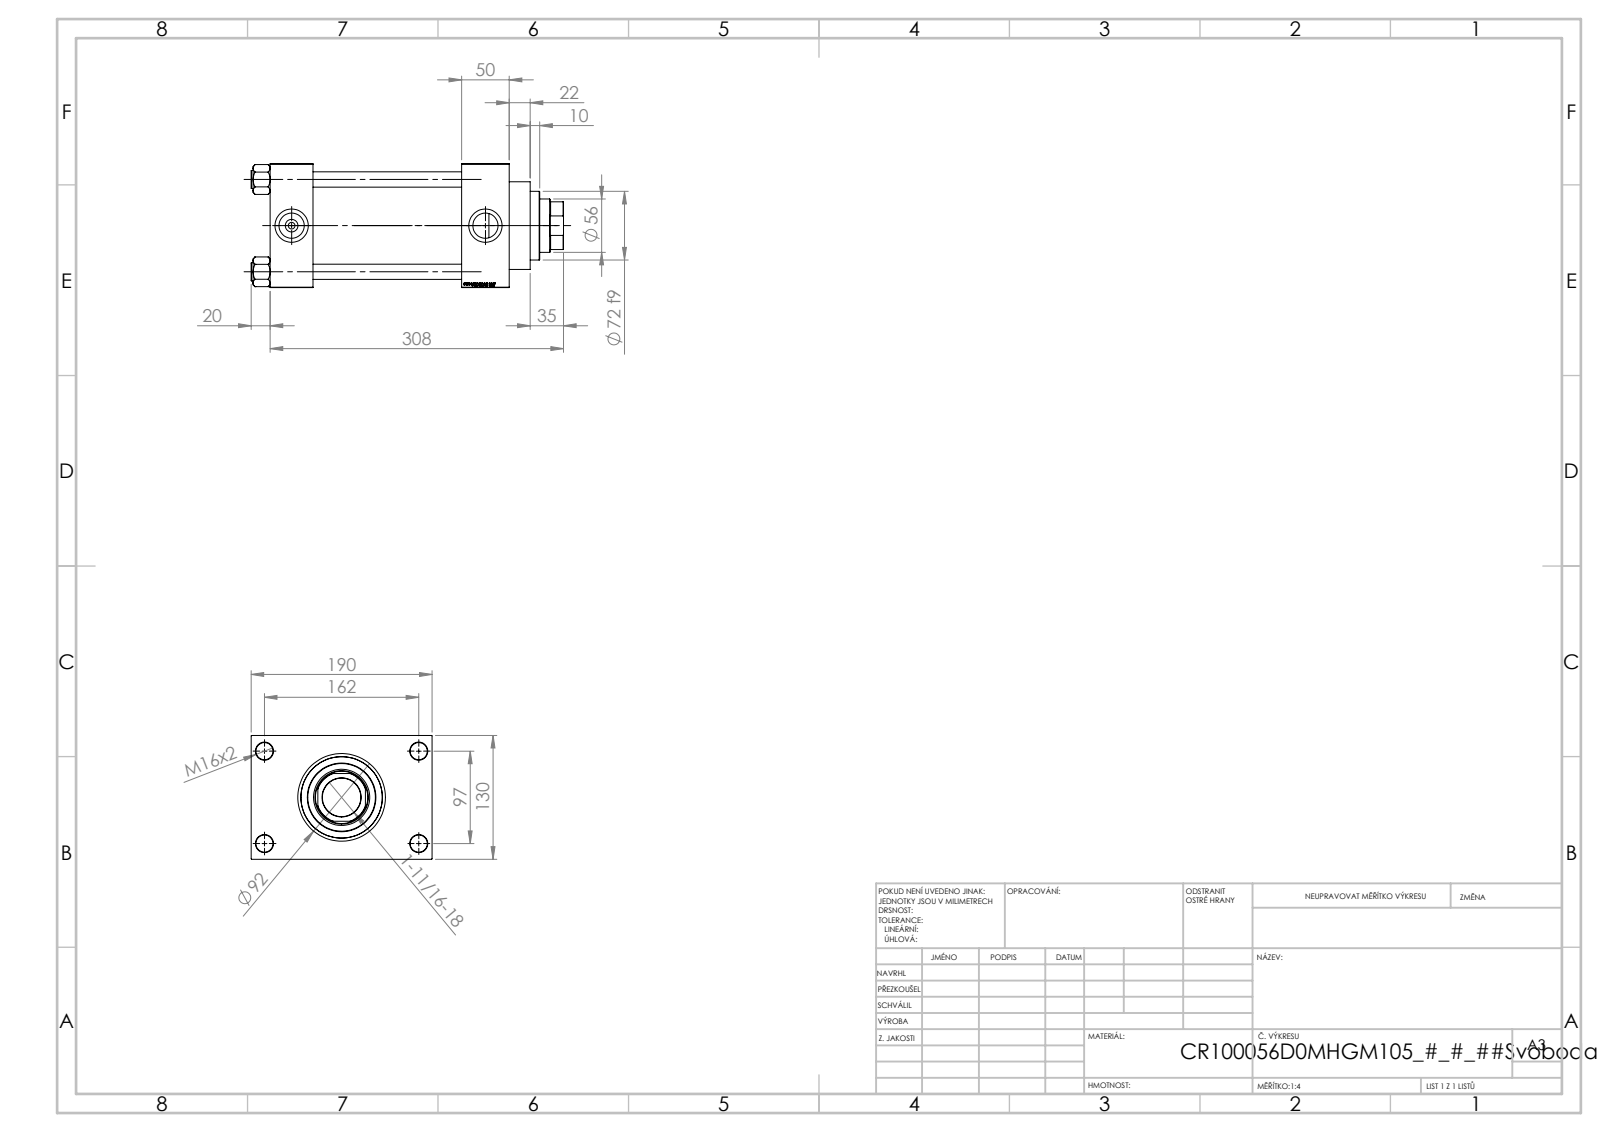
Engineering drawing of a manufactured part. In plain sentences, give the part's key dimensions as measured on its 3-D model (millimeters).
The part is named "NUT_M5_D; V215CR_VCP_D; V215CR_D_TYCINKA; V215_VC_A (+1 more)". Its 3-D file was written by "SolidWorks 2019 (CONFIG_CONTROL_DESIGN)". It is 11 solids with 1151 faces: 545 planar, 88 cylindrical and 518 other. Overall it measures 328 by 190 by 130 millimeters. Its volume is 2 988 000 cubic millimeters and its surface area 449 417 square millimeters. Round holes: 4 of diameter 16, 4 of diameter 18, 2 of diameter 7, 2 of diameter 26.44, 2 of diameter 35, 1 of diameter 40.5, 1 of diameter 56, 1 of diameter 59, 1 of diameter 76, 1 of diameter 85.5, 1 of diameter 100. Round bosses or shafts: 4 of diameter 19, 1 of diameter 106, 1 of diameter 92, 1 of diameter 72. Partial cylindrical surfaces (rounded edges, fillets, slot ends): 1 of radius 27. The main face-to-face distances are 130, 50, 45, 201, 156, 251, 206, 30, 160, 190. The hole center spacings are 32.55, 68.52, 94.41, 96.9, 102.27, 129.45, 161.73, 97.
